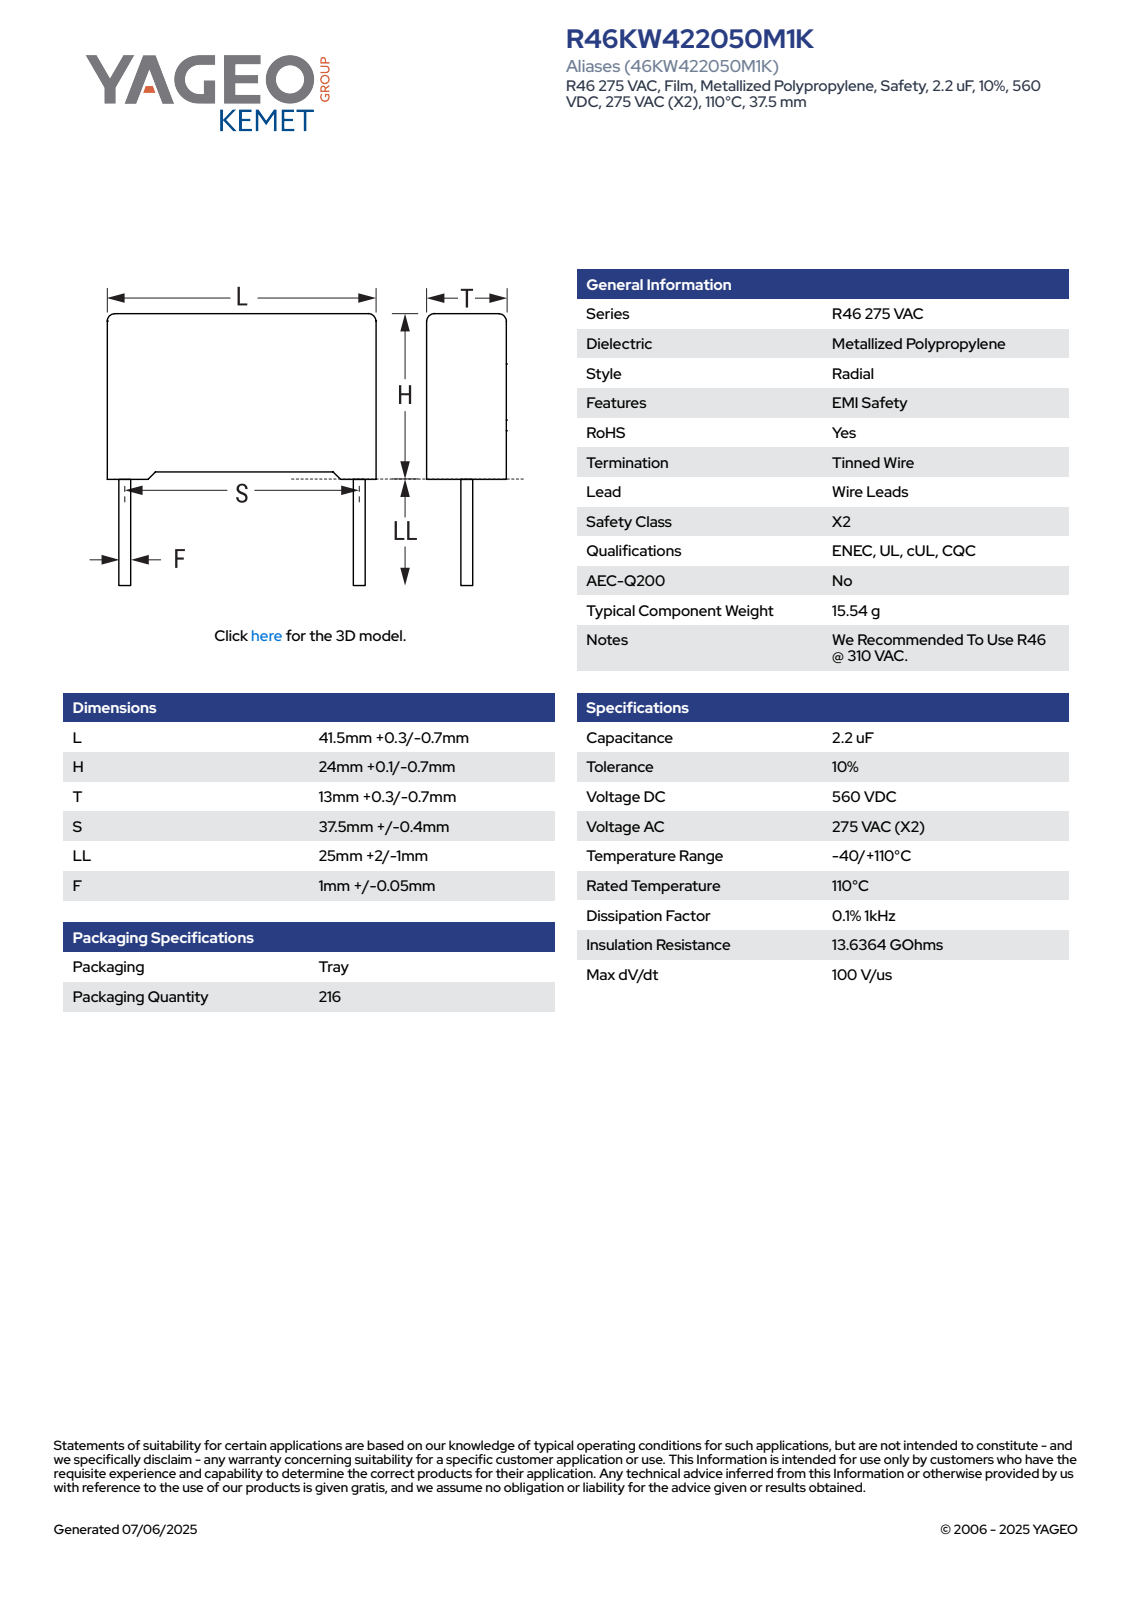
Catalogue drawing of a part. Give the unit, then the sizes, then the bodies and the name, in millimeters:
Units: millimetres
Overall size (bounding box): 51.1 × 41.8 × 13.3
Round bosses / shafts (diameter × count): ⌀1.05 ×2
Partial cylindrical surfaces — rounded edges, fillets, slot ends (radius × count): R0.5 ×4
Main face-to-face distances: 13.3, 23.27, 41.8, 23.35, 0.75, 0.83, 24.1, 13.31, 1.39, 40.41
Volume: 13 028 mm³ · Surface area: 4 028 mm²
Bodies: 4 solids, 85 faces (77 planar, 8 cylindrical, 0 other)
Part name (STEP PRODUCT): CFR_RB2_41.5X24X13_L41.8H24.1T13.3S37.5LL27F1.05
STEP written by: SolidWorks 2021 (AUTOMOTIVE_DESIGN)
